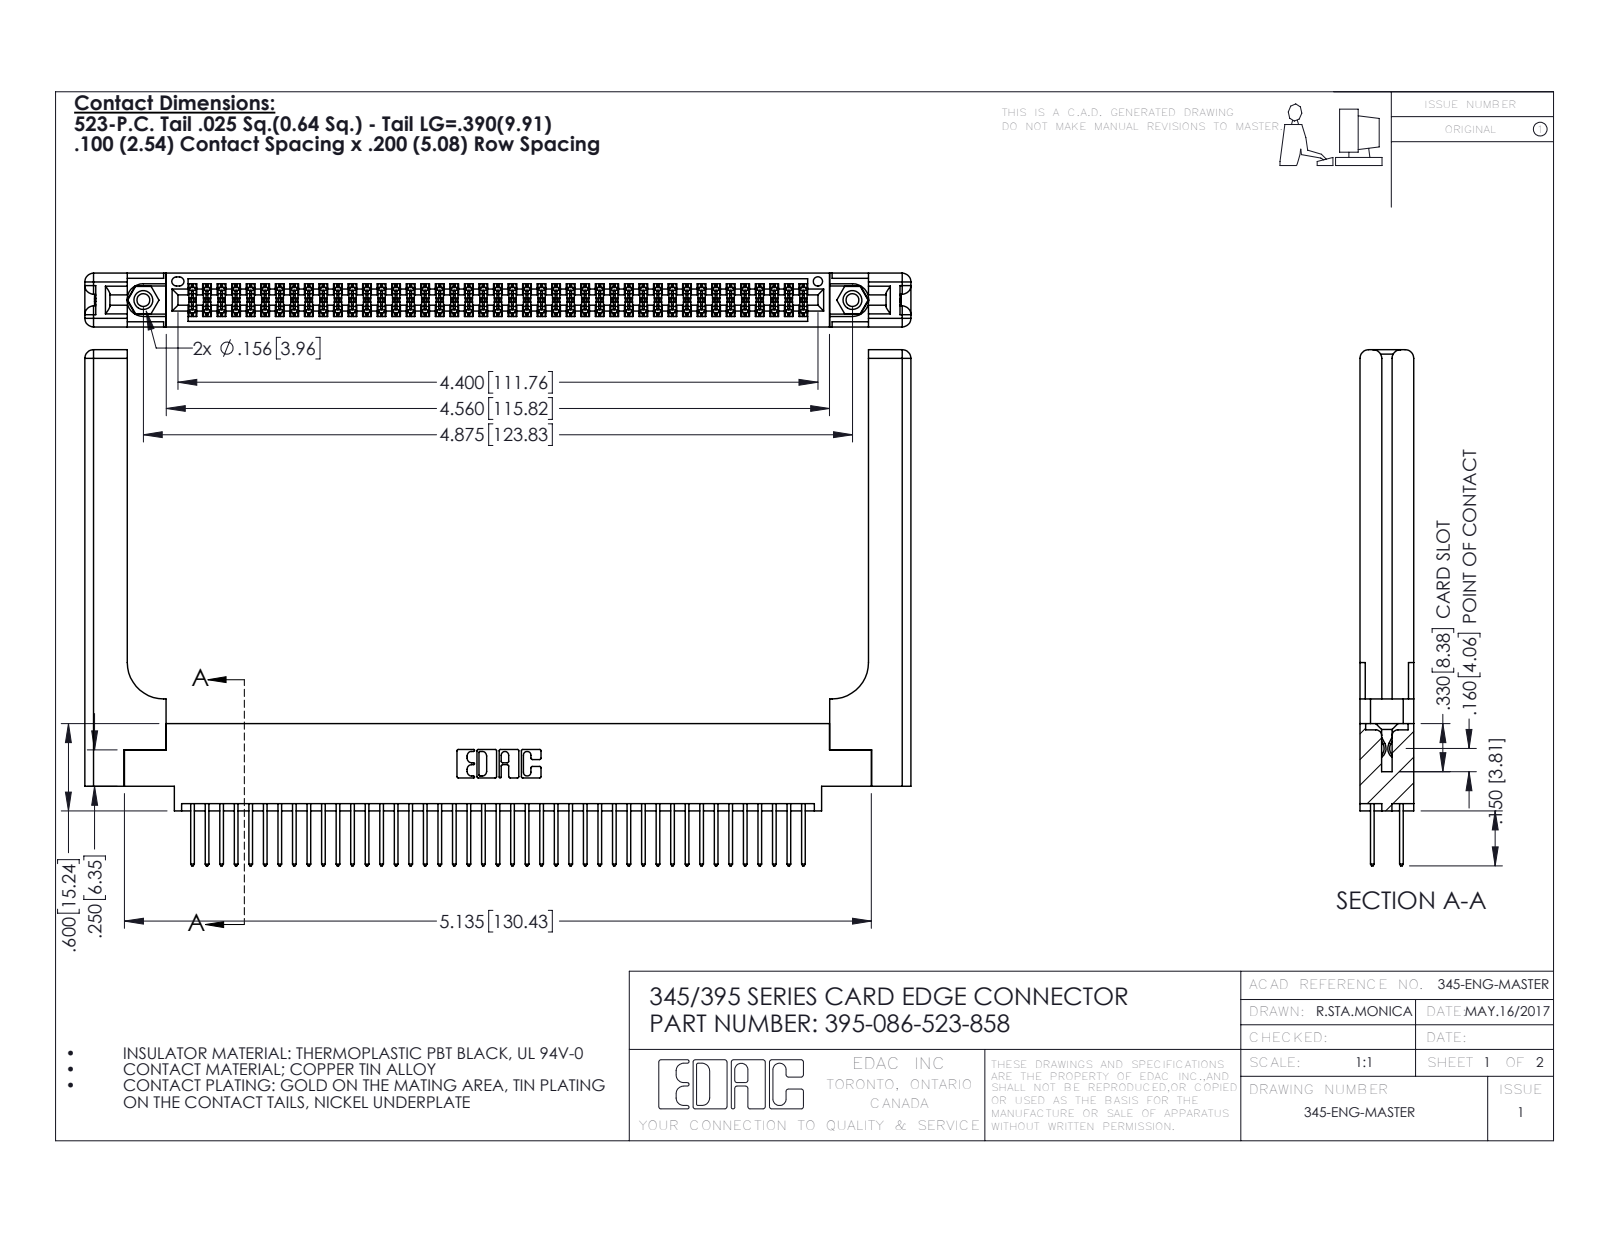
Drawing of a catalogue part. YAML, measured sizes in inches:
part_name: "345-220-058_345-220-058; 395-086-523-858; 345-250-001_345-250-001-102; 345 Part_0.170 Offset - 0.156 Dia-TH (+1 more)"
step_written_by: "SolidWorks 2016 (CONFIG_CONTROL_DESIGN)"
units: inches
bodies: {solids: 91, faces: 4686, planar: 3070, cylindrical: 1556, other: 60}
overall_size: [5.679, 3.547, 0.37]
volume: 1.377
surface_area: 41.59
round_holes:
  - {diameter: 0.089, count: 2}
  - {diameter: 0.125, count: 2}
  - {diameter: 0.156, count: 2}
  - {diameter: 0.064, count: 1}
round_bosses_or_shafts:
  - {diameter: 0.155, count: 2}
partial_cylinders:
  - {radius: 0.006, count: 129}
  - {radius: 0.01, count: 86}
  - {radius: 0.01, count: 22}
  - {radius: 0.06, count: 16}
  - {radius: 0.007, count: 6}
  - {radius: 0.031, count: 6}
  - {radius: 0.026, count: 3}
  - {radius: 0.014, count: 2}
face_to_face_distances: [0.072, 0.298, 0.37, 0.098, 0.272, 0.025, 0.2, 0.225, 0.175, 0.148]
hole_center_spacings: [0.27, 4.639, 4.875]
